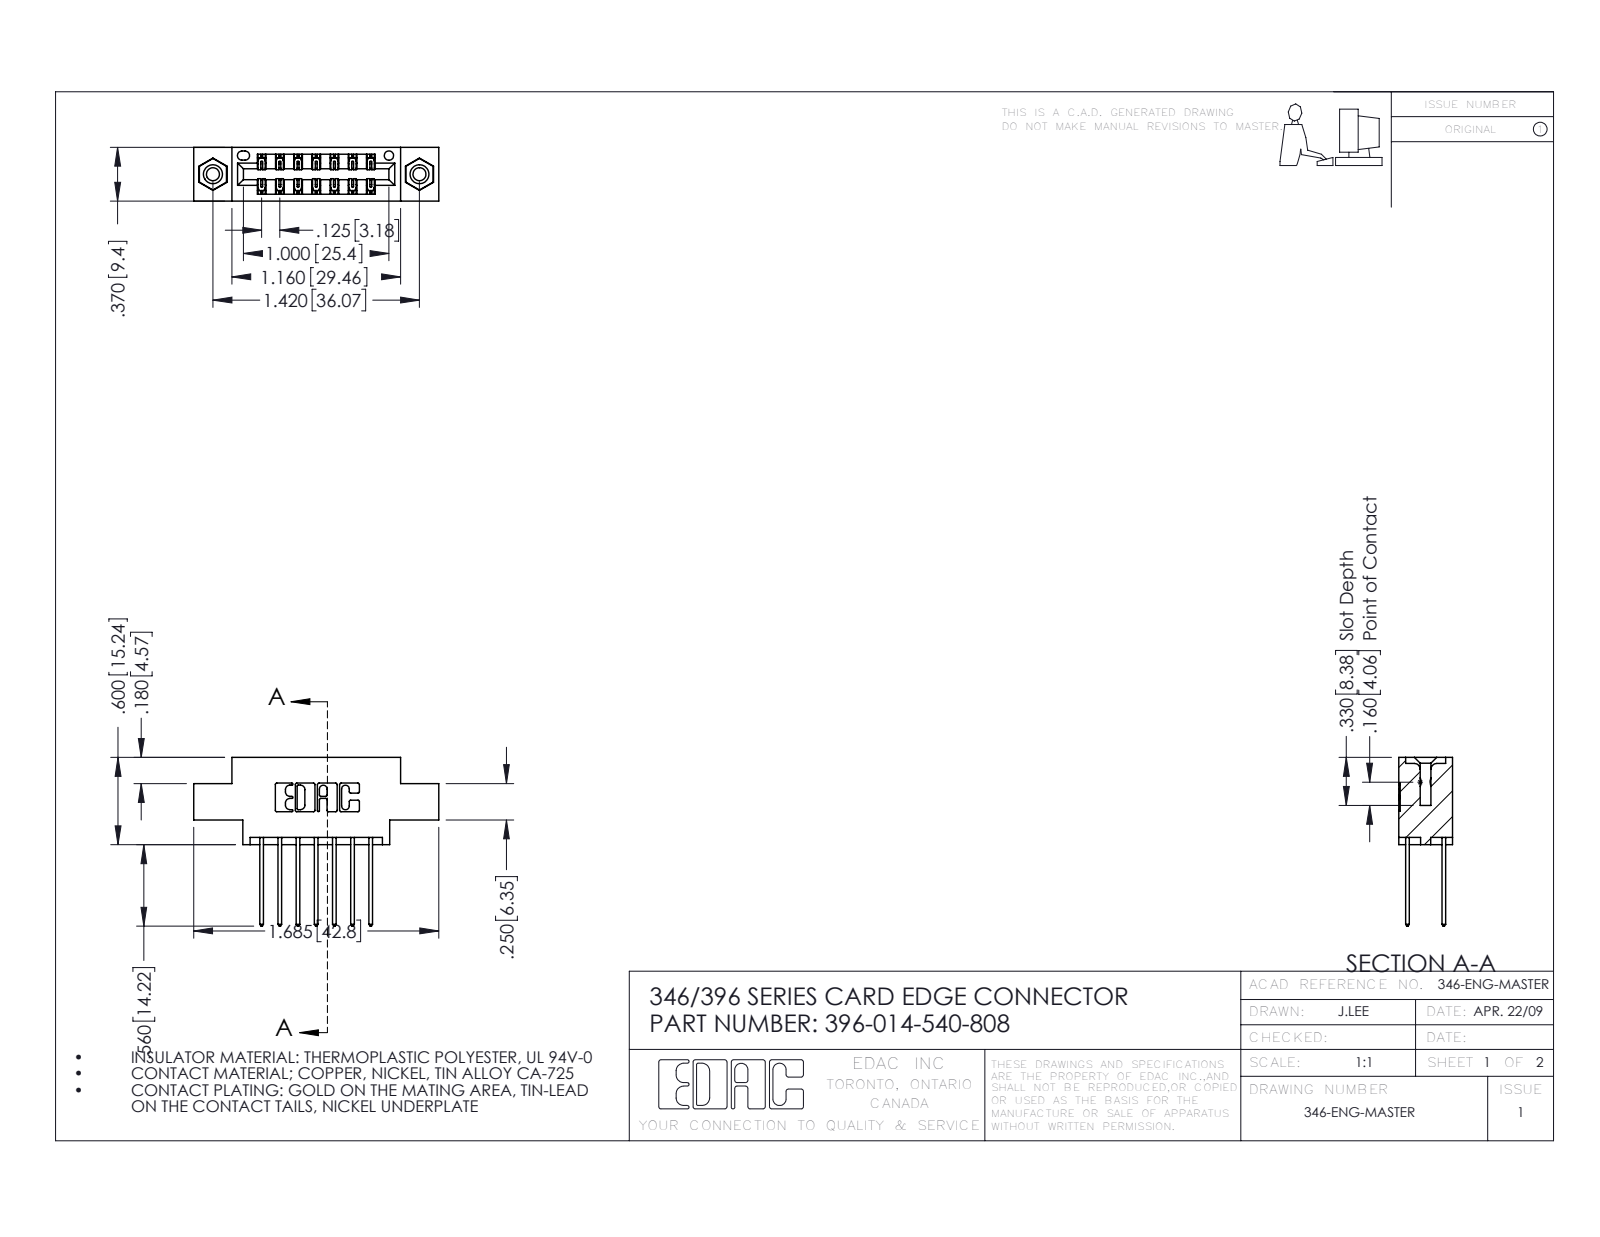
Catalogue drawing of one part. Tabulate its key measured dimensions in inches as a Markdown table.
| quantity | value |
| --- | --- |
| part name | 345-292-001_345-293-140; 345-250-001_345-250-003-102; 396-014-540-808; 346 Part_0.170 Offset - 0.156 Dia-TI |
| STEP written by | SolidWorks 2016 (CONFIG_CONTROL_DESIGN) |
| units | inches |
| bodies | 17 solids, 914 faces (602 planar, 296 cylindrical, 16 other) |
| overall size | 1.685 × 1.16 × 0.37 |
| volume | 0.231 in³ |
| surface area | 7.928 in² |
| round holes (diameter × count) | 0.089 × 2, 0.125 × 2, 0.156 × 2, 0.064 × 1 |
| round bosses / shafts (diameter × count) | 0.155 × 2 |
| partial cylindrical surfaces (radius × count) | 0.01 × 22, 0.006 × 21, 0.01 × 14, 0.007 × 6, 0.031 × 6, 0.026 × 3, 0.014 × 2, 0.022 × 2 |
| main face-to-face distances | 0.25, 0.048, 0.322, 0.37, 0.072, 0.298, 0.025, 0.275, 0.222, 0.148 |
| hole center spacings | 0.246, 1.217, 1.42 |
